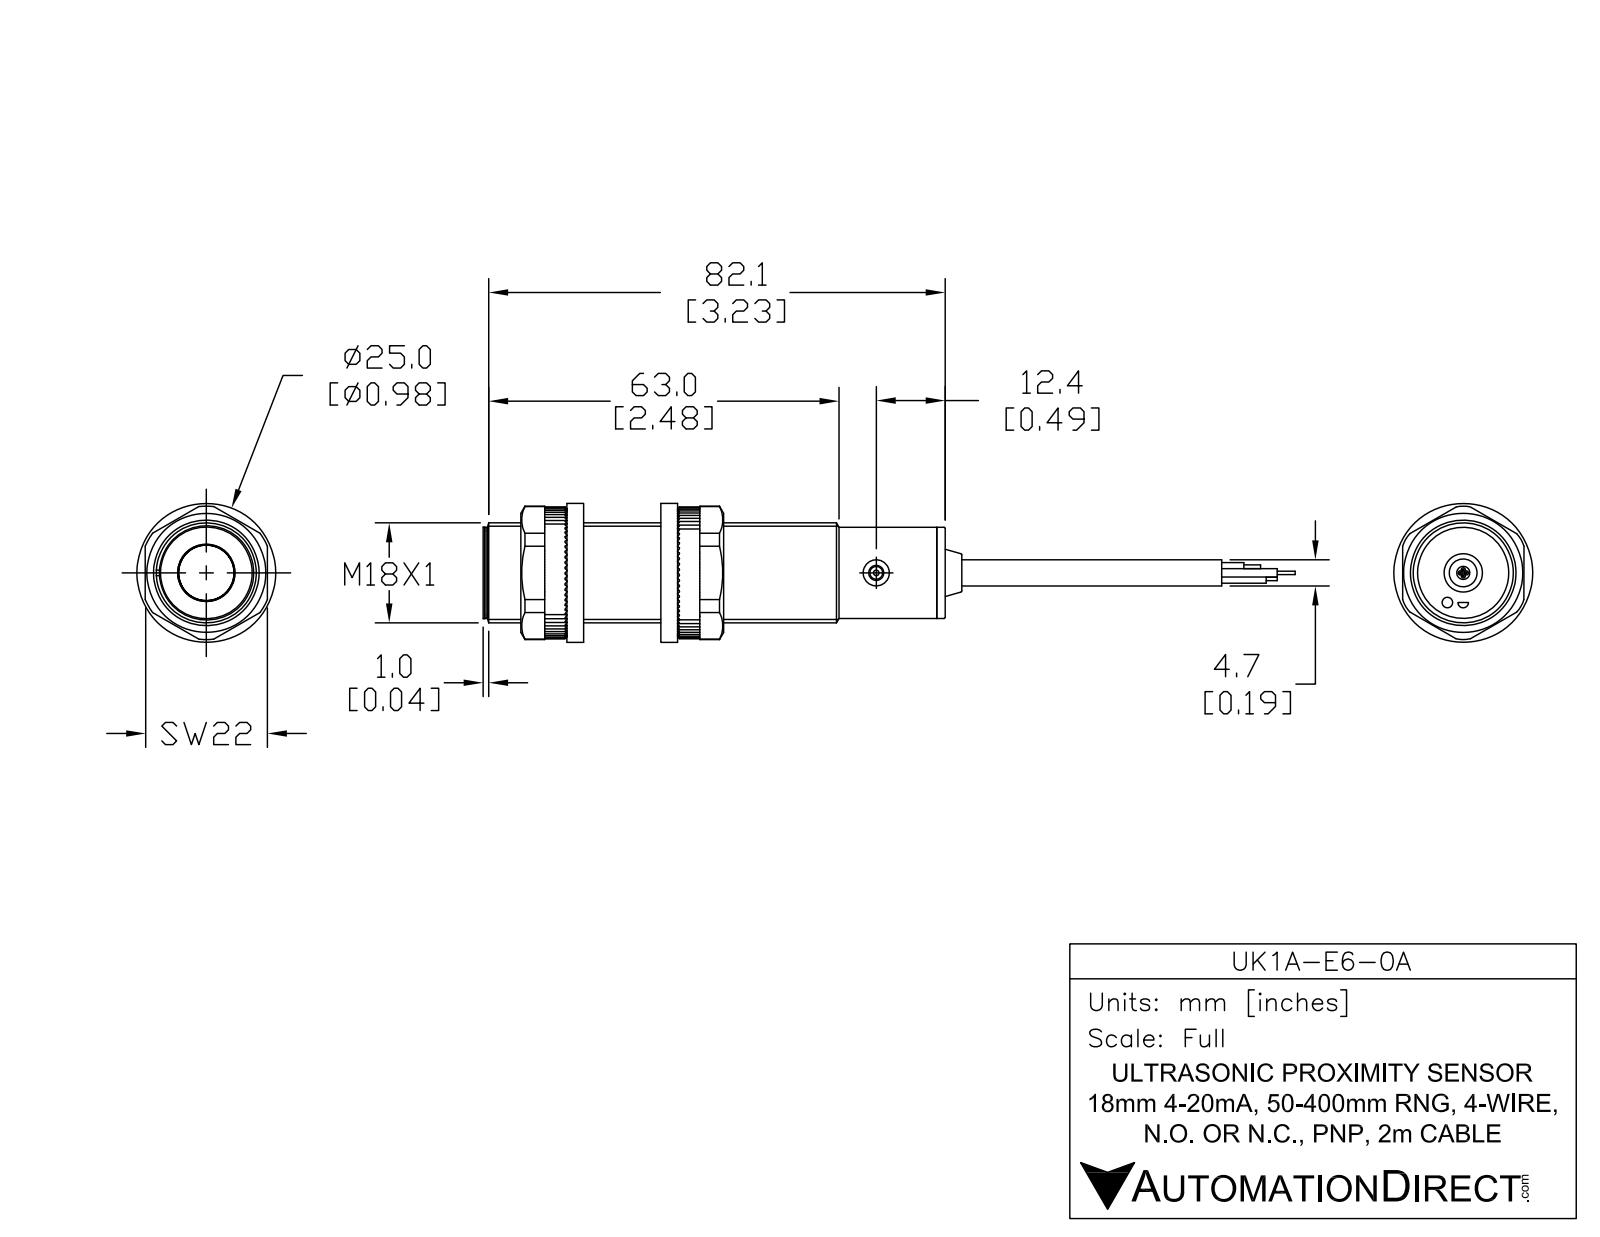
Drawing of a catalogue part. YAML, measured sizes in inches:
part_name: "UK1A-E6-0A"
step_written_by: "SolidWorks 2017 (AUTOMOTIVE_DESIGN)"
units: inches
bodies: {solids: 6, faces: 55, planar: 17, cylindrical: 24, other: 14}
overall_size: [4.832, 0.709, 0.709]
volume: 1.285
surface_area: 10.69
round_holes:
  - {diameter: 0.185, count: 2}
  - {diameter: 0.106, count: 1}
round_bosses_or_shafts:
  - {diameter: 0.709, count: 1}
  - {diameter: 0.646, count: 1}
  - {diameter: 0.622, count: 1}
  - {diameter: 0.374, count: 1}
  - {diameter: 0.189, count: 1}
  - {diameter: 0.091, count: 1}
face_to_face_distances: [3.193, 3.252, 0.059, 0.039, 3.232, 3.291, 0.041, 3.234, 3.293, 3.257]
